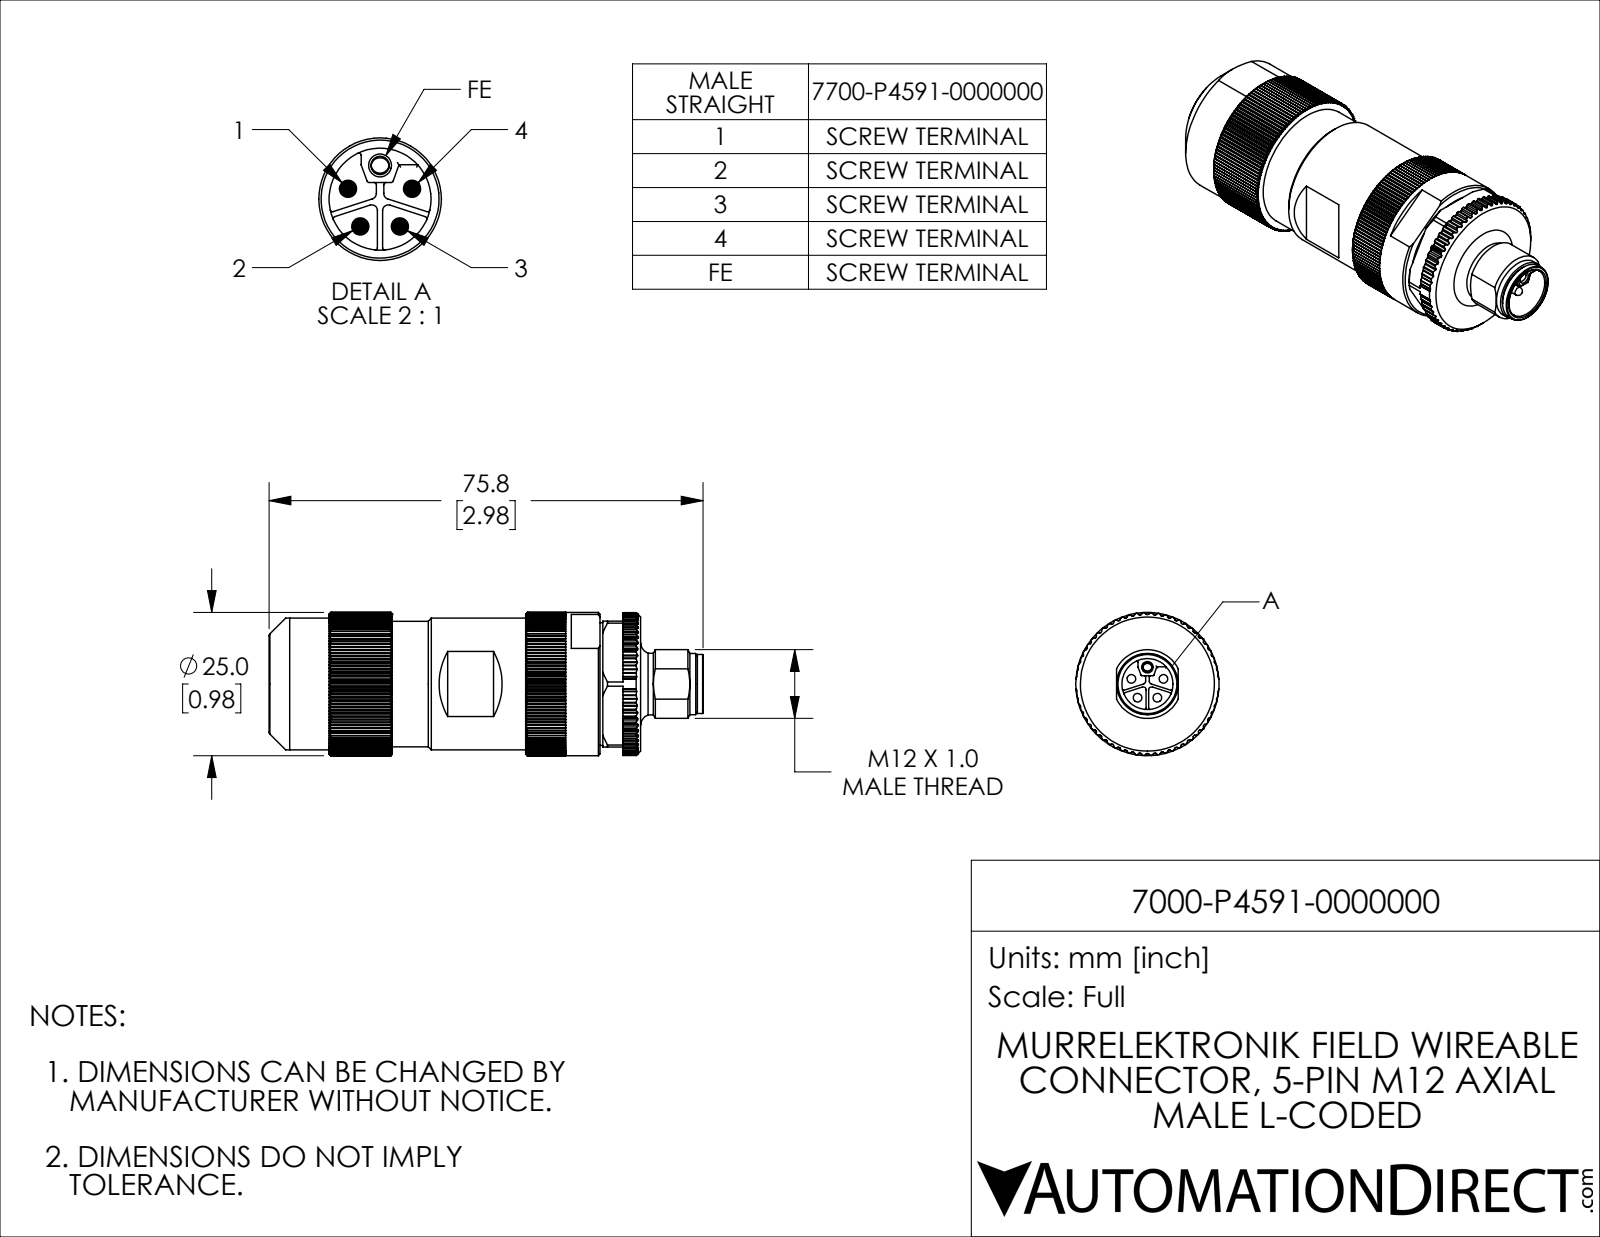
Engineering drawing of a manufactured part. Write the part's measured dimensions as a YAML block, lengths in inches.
part_name: "7000-P4591-0000000"
step_written_by: "SolidWorks 2021 (CONFIG_CONTROL_DESIGN)"
units: inches
bodies: {solids: 1, faces: 1319, planar: 858, cylindrical: 361, other: 100}
overall_size: [2.984, 0.984, 0.984]
volume: 1.754
surface_area: 11.9
round_holes:
  - {diameter: 0.063, count: 1}
  - {diameter: 0.091, count: 1}
  - {diameter: 0.35, count: 1}
  - {diameter: 0.52, count: 1}
round_bosses_or_shafts:
  - {diameter: 0.059, count: 4}
  - {diameter: 0.984, count: 1}
  - {diameter: 0.906, count: 1}
  - {diameter: 0.863, count: 1}
  - {diameter: 0.843, count: 1}
  - {diameter: 0.424, count: 1}
  - {diameter: 0.421, count: 1}
  - {diameter: 0.406, count: 1}
partial_cylinders:
  - {radius: 0.012, count: 82}
  - {radius: 0.008, count: 74}
  - {radius: 0.02, count: 4}
  - {radius: 0.031, count: 2}
  - {radius: 0.043, count: 2}
  - {radius: 0.006, count: 1}
  - {radius: 0.236, count: 1}
  - {radius: 0.48, count: 1}
face_to_face_distances: [2.503, 0.02, 0.866, 2.224, 0.28, 0.787, 0.794, 1.429, 1.709, 0.886]
hole_center_spacings: [0.116]
